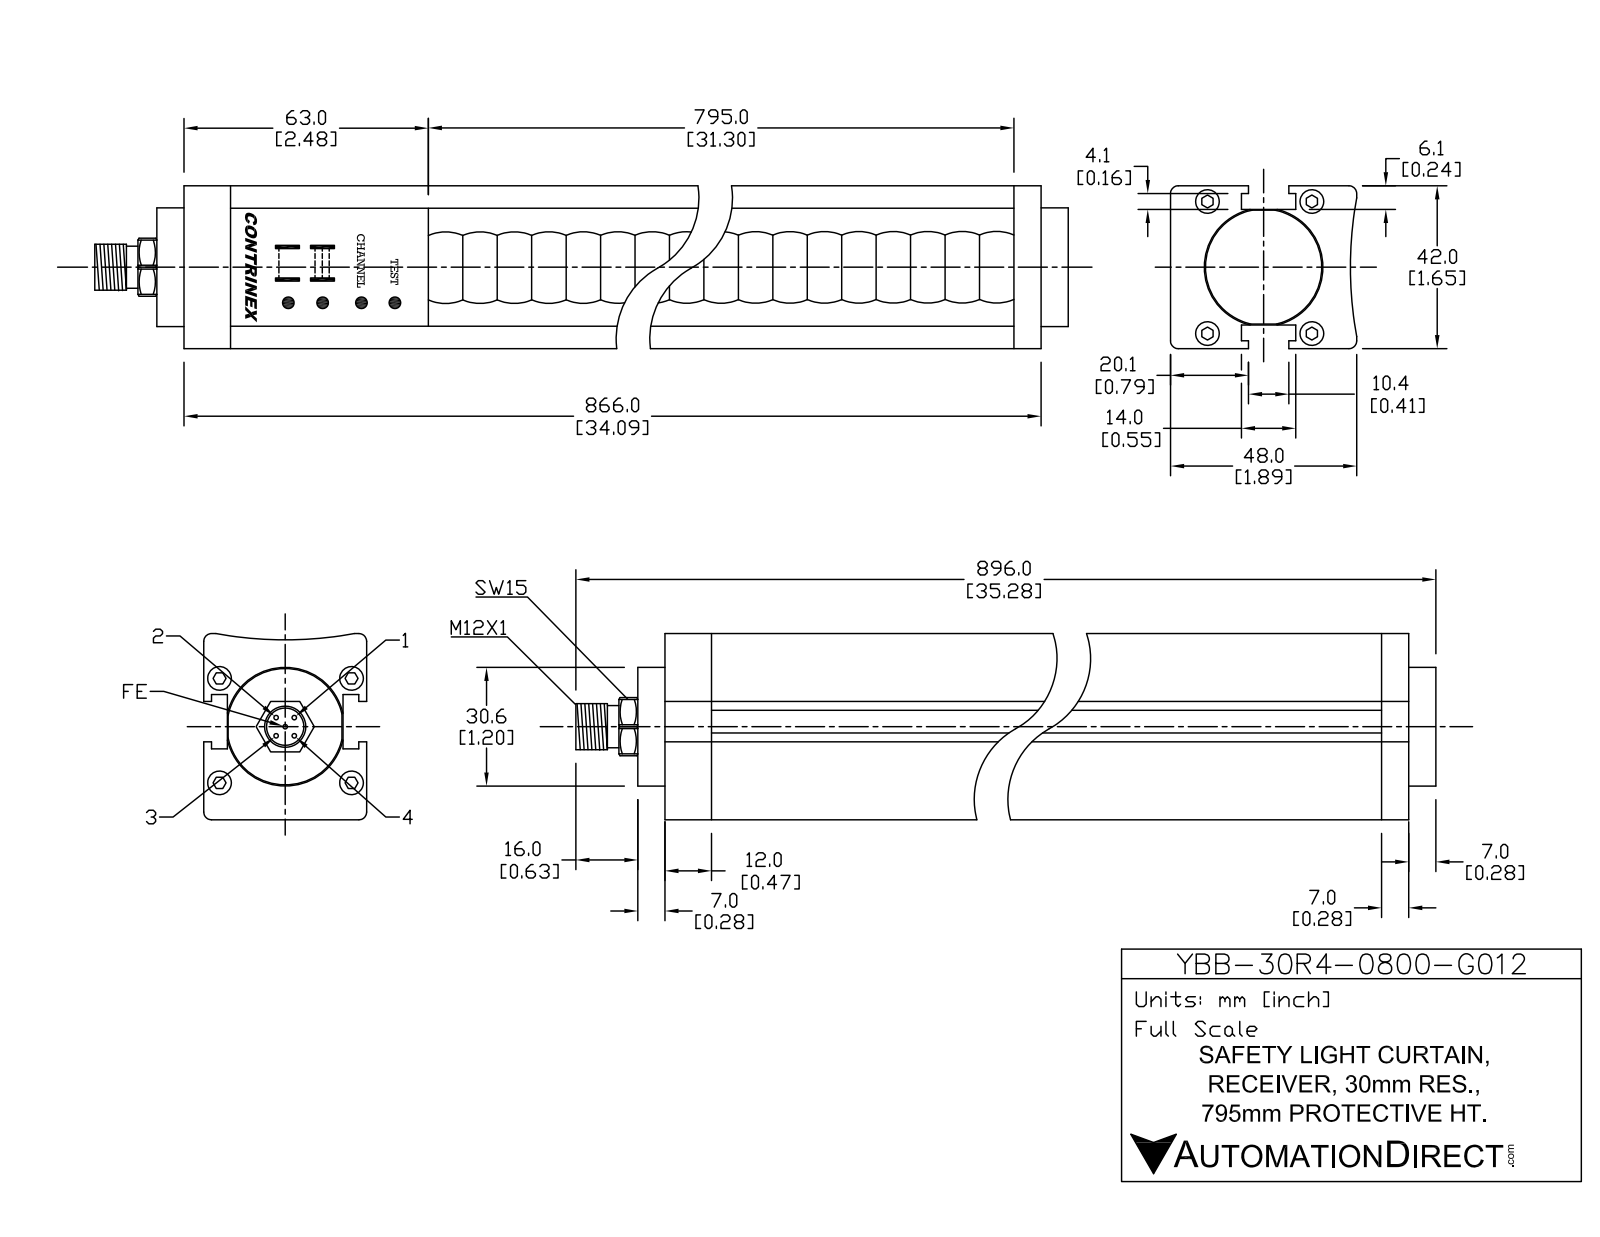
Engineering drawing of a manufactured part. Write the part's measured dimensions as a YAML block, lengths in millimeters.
part_name: "YBB-30R4-0800-G012"
step_written_by: "SolidWorks 2016 (AUTOMOTIVE_DESIGN)"
units: millimeters
bodies: {solids: 19, faces: 440, planar: 208, cylindrical: 168, other: 64}
overall_size: [896, 48, 42]
volume: 1561000
surface_area: 202395
round_holes:
  - {diameter: 6, count: 4}
  - {diameter: 8.5, count: 1}
  - {diameter: 32, count: 1}
round_bosses_or_shafts:
  - {diameter: 1, count: 5}
  - {diameter: 5.5, count: 4}
  - {diameter: 30.6, count: 1}
  - {diameter: 12, count: 1}
  - {diameter: 10.5, count: 1}
partial_cylinders:
  - {radius: 1, count: 48}
  - {radius: 0.5, count: 4}
  - {radius: 0.55, count: 2}
  - {radius: 8.2, count: 1}
  - {radius: 100, count: 1}
face_to_face_distances: [6.3, 35.7, 42, 29.4, 14, 17.2, 31.2, 15.7, 29.7, 46.9]
hole_center_spacings: [21.04, 22.34, 26.9, 34, 43.35]
